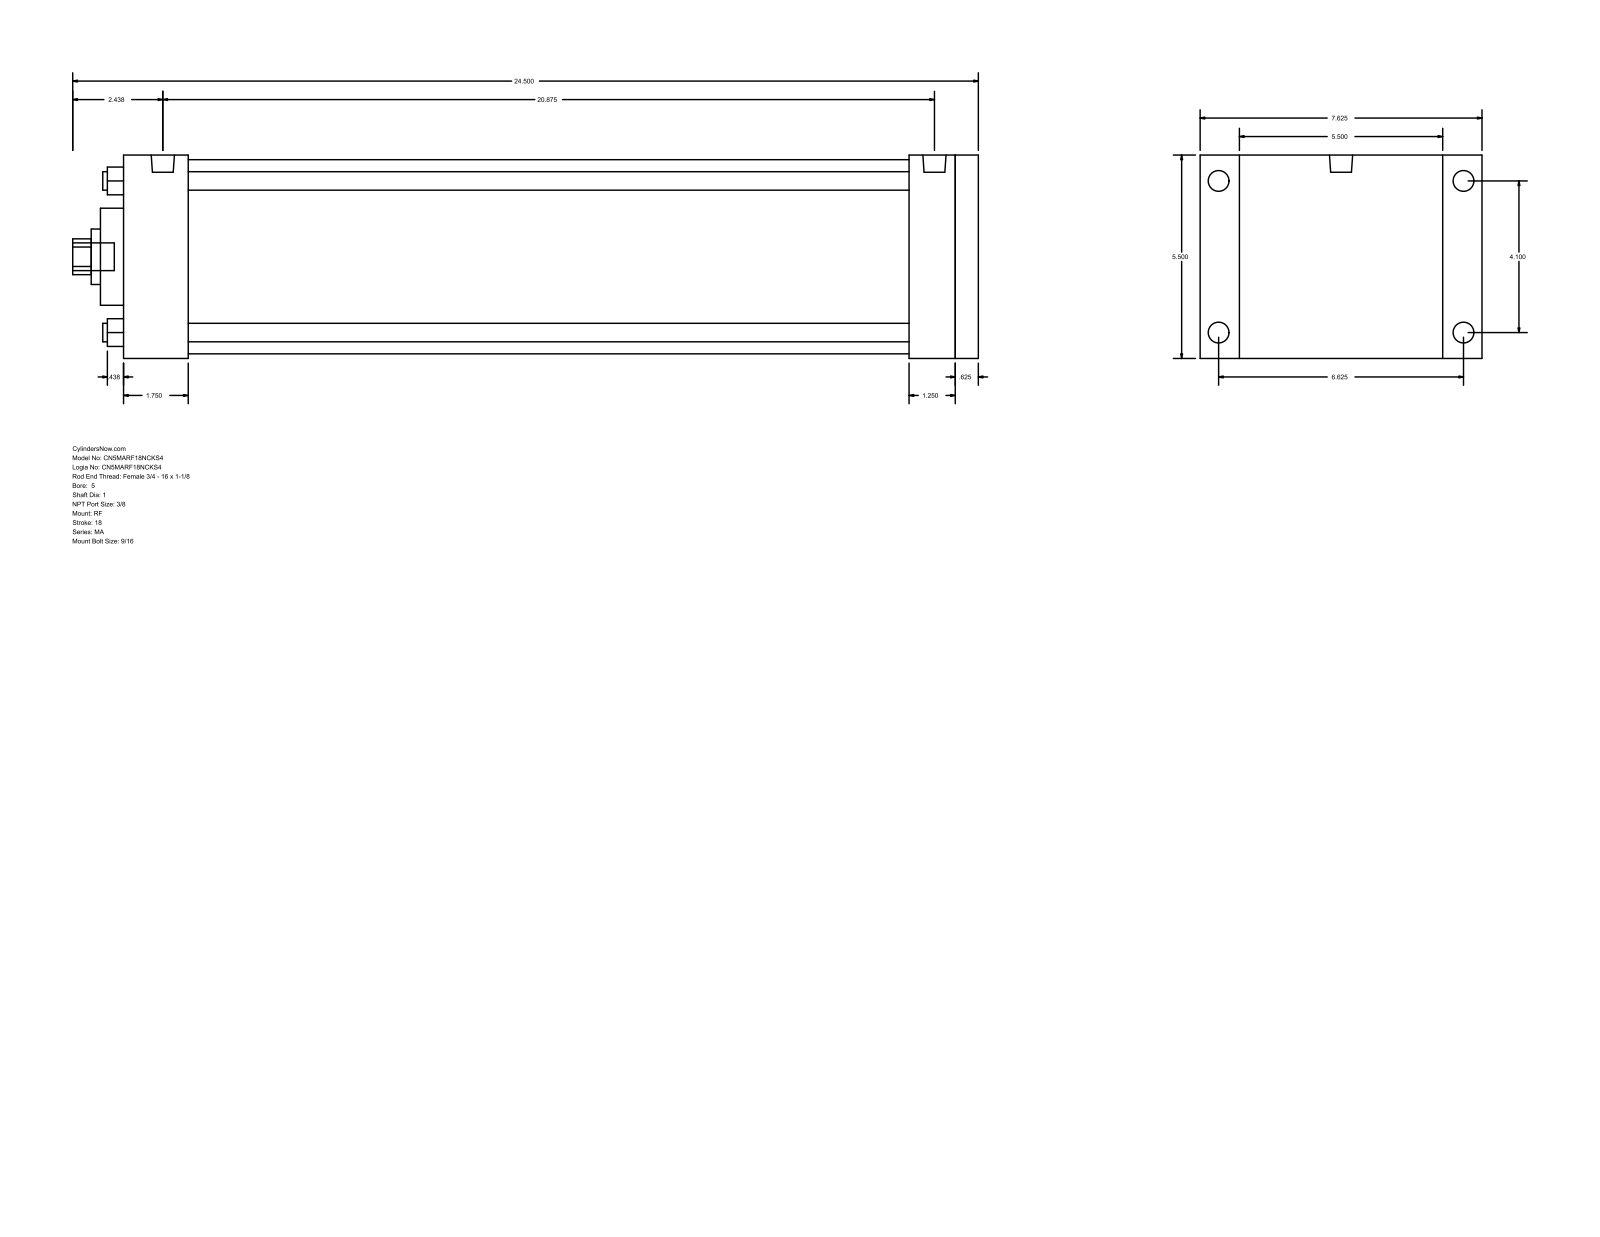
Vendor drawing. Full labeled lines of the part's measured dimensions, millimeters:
Part name (STEP PRODUCT): MA_RF__0500_1
STEP written by: GSSL Pune (CONFIG_CONTROL_DESIGN)
Units: millimetres
Bodies: 0 solids, 94 faces (65 planar, 29 cylindrical, 0 other)
Overall size (bounding box): 622.3 × 193.68 × 139.7
Round holes (diameter × count): ⌀12.7 ×4, ⌀25.4 ×1, ⌀38.1 ×1, ⌀66.67 ×1, ⌀133.35 ×1
Round bosses / shafts (diameter × count): ⌀14.29 ×4, ⌀11.11 ×4, ⌀15.93 ×2, ⌀19.05 ×1
Partial cylindrical surfaces — rounded edges, fillets, slot ends (radius × count): R12.29 ×1
Main face-to-face distances: 139.7, 587.38, 571.5, 15.88, 44.46, 527.04, 542.92, 539.75, 495.29, 31.75
Hole centre spacings: 73.64, 104.14, 147.28
